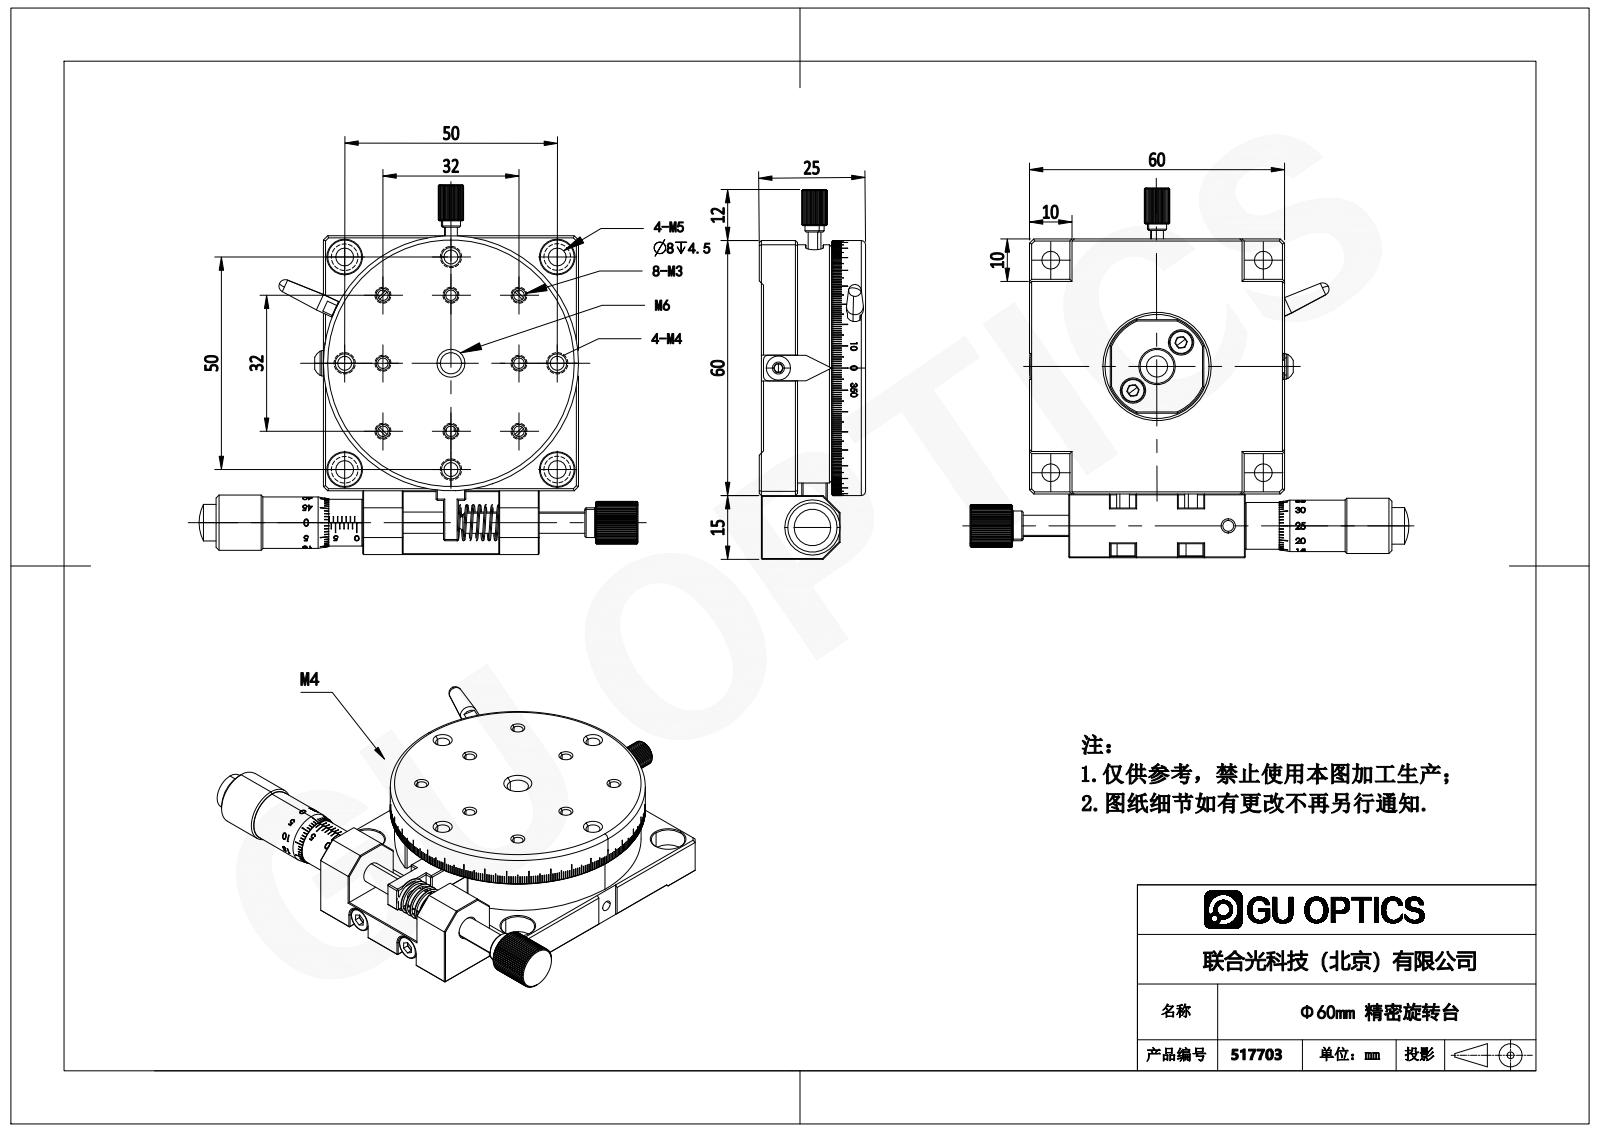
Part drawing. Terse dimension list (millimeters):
name: SEMR60-AR
written by: SolidWorks 2020 (CONFIG_CONTROL_DESIGN)
unit: mm
bodies: 2 solids, 3498 faces (2806 planar, 307 cylindrical, 385 other)
size: 103.25 × 87 × 25
volume: 72 405 mm³; area: 30 131 mm²
holes: 12× ⌀2.5, 5× ⌀3.5, 5× ⌀8, 4× ⌀3.3, 4× ⌀4.2, 2× ⌀3.4, 2× ⌀6, 1× ⌀2.6, 1× ⌀5, 1× ⌀8.5, 1× ⌀9.5, 1× ⌀10
bosses: 7× ⌀3, 2× ⌀5.6, 2× ⌀5.5, 1× ⌀60, 1× ⌀58, 1× ⌀20, 1× ⌀19.4, 1× ⌀13
rounds: 2× R1, 2× R2, 2× R3, 1× R5, 1× R5.49, 1× R6.04, 1× R12, 1× R29.99
face distances: 8.5, 7.5, 24.5, 16, 17, 8, 0.5, 1.5, 16.5, 10
hole spacings: 16, 25, 18.36, 22.63, 26.57, 29.68, 35.36, 35.78
